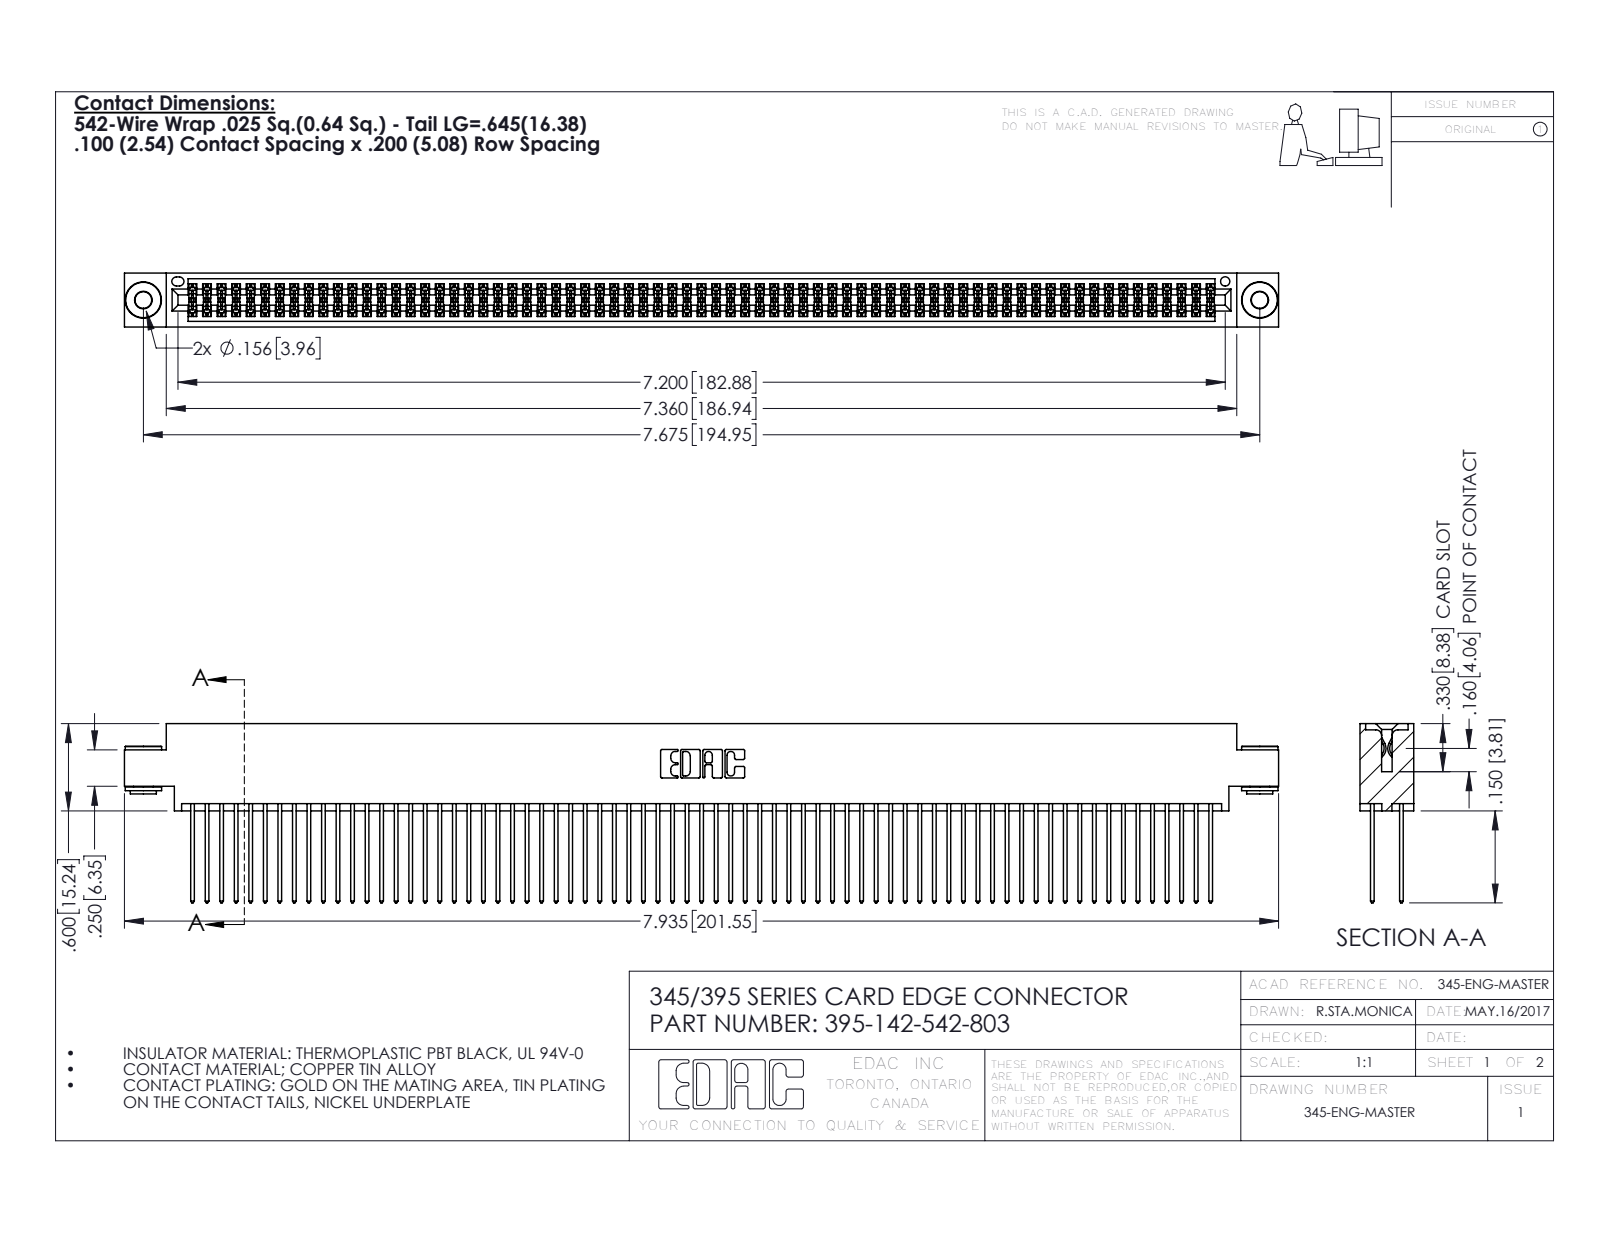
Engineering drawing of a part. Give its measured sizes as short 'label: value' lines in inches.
name: 345-292-001_345-293-142; 345 Part_0.170 Offset - 0.156 Dia-TH; 345-250-002_345-250-002-102; 395-142-542-803
written by: SolidWorks 2016 (CONFIG_CONTROL_DESIGN)
unit: in
bodies: 145 solids, 7268 faces (4780 planar, 2480 cylindrical, 8 other)
size: 7.935 × 1.232 × 0.37
volume: 1.246 in³; area: 52.98 in²
holes: 2× ⌀0.116, 2× ⌀0.156, 1× ⌀0.064
bosses: 2× ⌀0.25, 2× ⌀0.18, 2× ⌀0.136
rounds: 213× R0.006, 142× R0.01, 22× R0.01, 6× R0.007, 6× R0.031, 3× R0.026, 2× R0.014, 2× R0.019
face distances: 0.072, 0.298, 0.2, 0.098, 0.272, 0.025, 0.37, 0.225, 0.175, 0.149
hole spacings: 0.27, 7.439, 7.675
